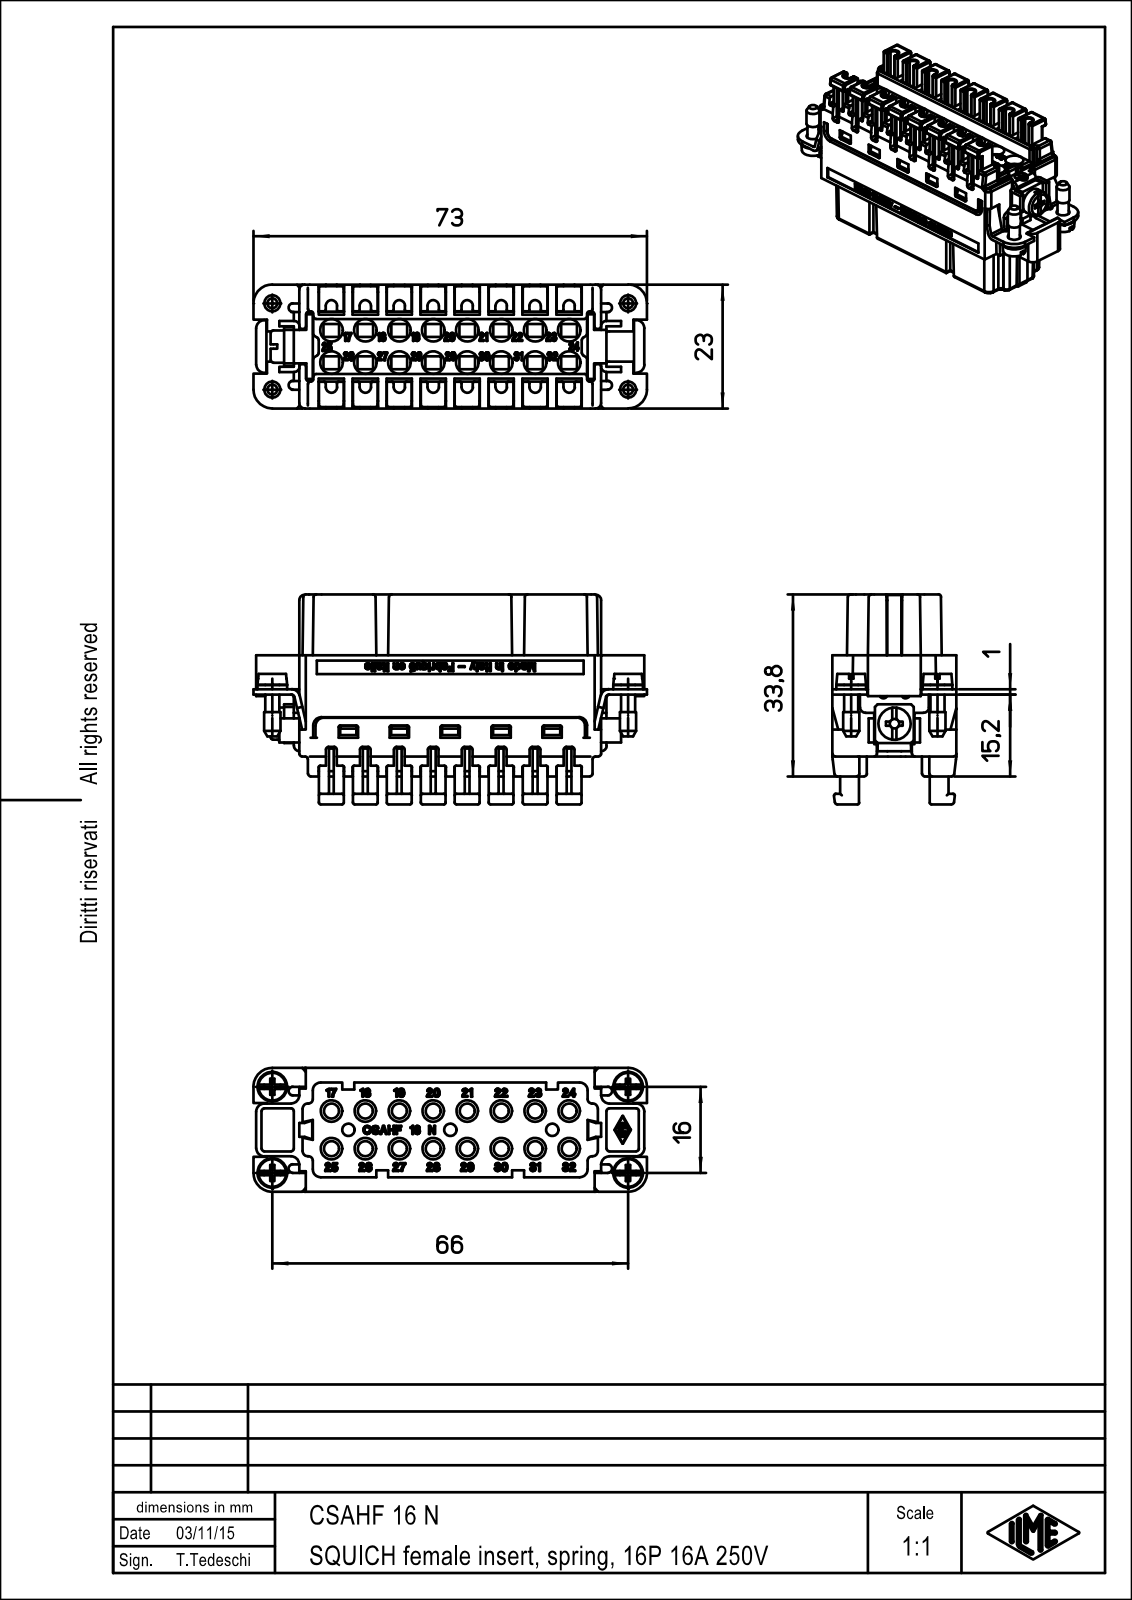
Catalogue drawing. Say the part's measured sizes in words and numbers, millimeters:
The part is named "CSAHF_16_N". Its 3-D file was written by "PTC Creo Elements/Direct Modeling 19.0B 21-Mar-2015 (C) Parametric Technology GmbH (AUTOMOTIVE_DESIGN)". It is 1 solid with 1900 faces: 1352 planar, 374 cylindrical and 174 other. Overall it measures 73 by 39 by 23 millimeters. Its volume is 37 378 cubic millimeters and its surface area 17 976 square millimeters. Round holes: 16 of diameter 2.8, 16 of diameter 4.2, 1 of diameter 3.5. Round bosses or shafts: 4 of diameter 5.5, 4 of diameter 3, 1 of diameter 6. Partial cylindrical surfaces (rounded edges, fillets, slot ends): 64 of radius 0.2, 32 of radius 0.5, 16 of radius 1, 16 of radius 1.05, 16 of radius 1.5, 8 of radius 0.8, 4 of radius 3.5, 2 of radius 0.3. The main face-to-face distances are 6.3, 12.6, 16.6, 1.45, 18.9, 8, 23, 4.95, 5, 3.55. The hole center spacings are 25.2, 6.3, 6.32, 9.05, 14.18, 12.6, 12.61, 31.5.
